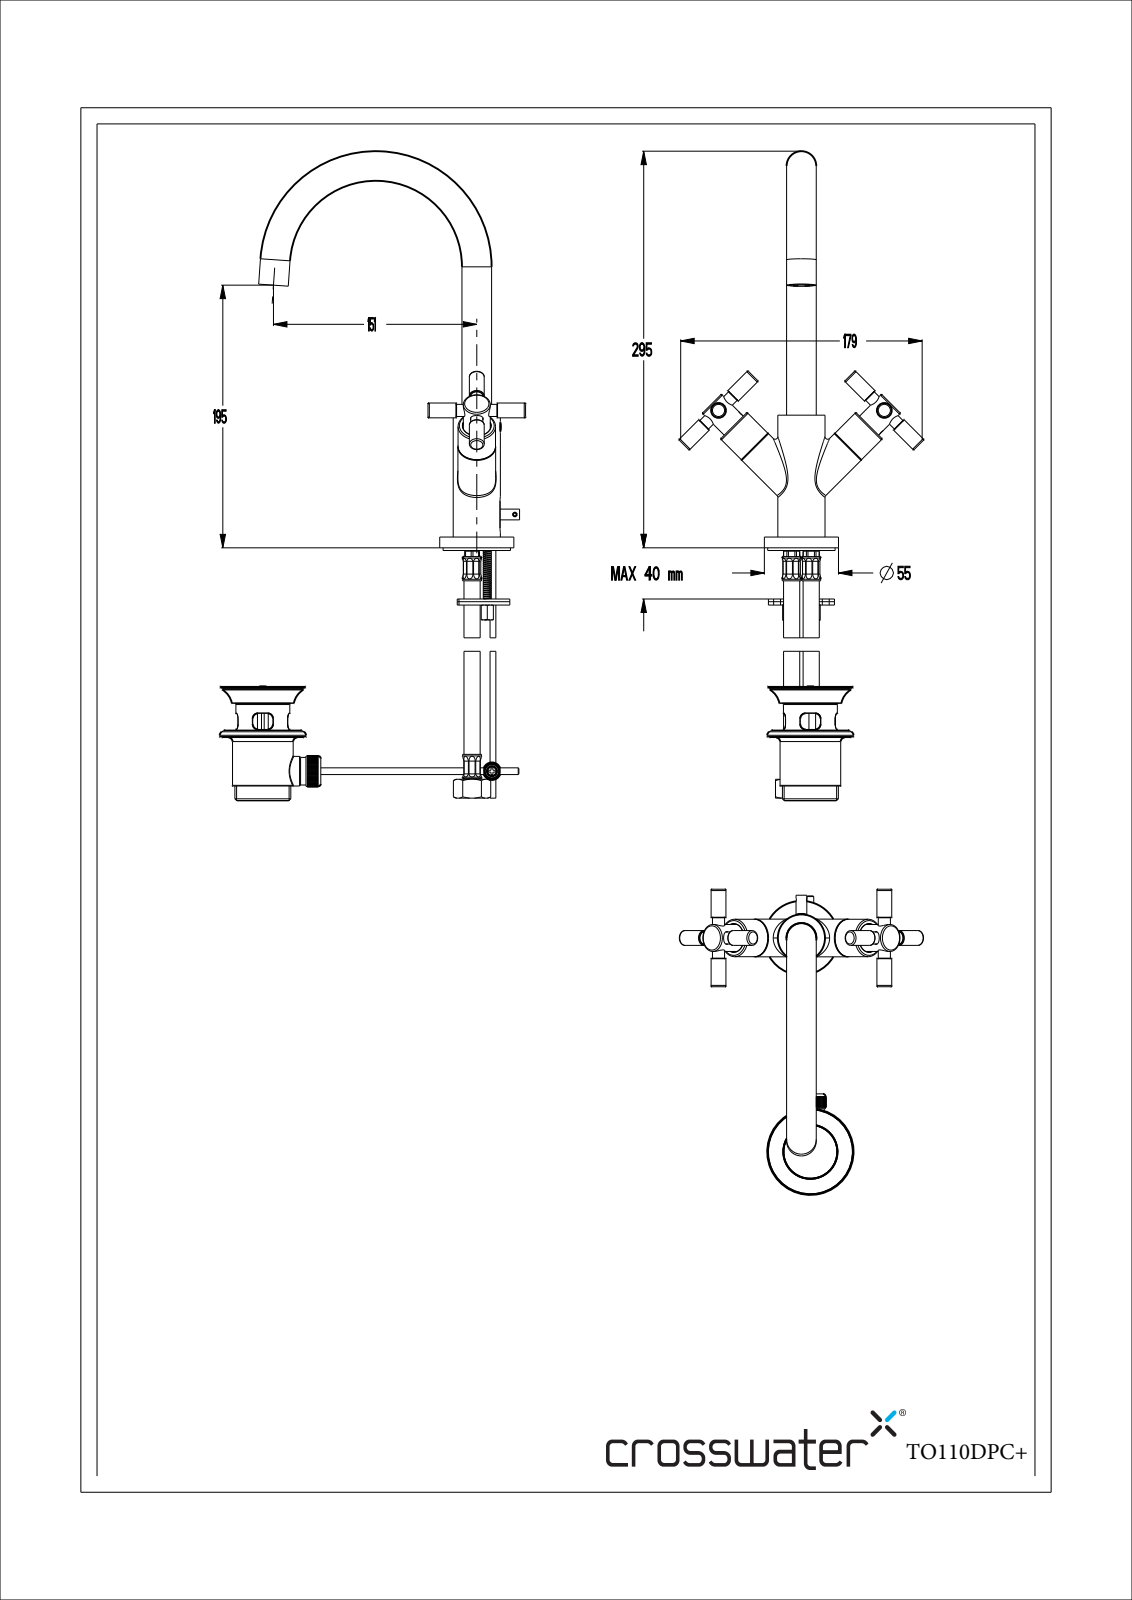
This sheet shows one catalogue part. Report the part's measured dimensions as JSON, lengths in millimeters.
{"part_name": "MSBR-42_1; MSBR-41_1; MSBR-36_2; MSBR-35_1 (+8 more)", "step_written_by": "PRO/ENGINEER BY PARAMETRIC TECHNOLOGY CORPORATION, 2009300 (CONFIG_CONTROL_DESIGN)", "units": "millimeters", "bodies": {"solids": 24, "faces": 842, "planar": 290, "cylindrical": 292, "other": 260}, "overall_size": [643, 198.04, 181.18], "volume_mm3": 169936, "surface_area_mm2": 115456, "round_holes": [[4.8, 4], [9.3, 4], [3.2, 2], [5, 2], [6, 2], [7, 2], [9, 2], [11, 2], [16, 2], [19, 2], [20, 2], [21, 2]], "round_bosses_or_shafts": [[11, 4], [9, 4], [6, 4], [4, 3], [28, 2], [27.8, 2], [22, 2], [20, 2]], "partial_cylinders_radius": [[2.85, 2], [3, 2], [9.55, 2], [3.3, 1], [8.5, 1]], "face_to_face_distances": [1, 6.5, 7, 97, 1.5, 90.5, 66.79, 0.5, 8, 45], "hole_center_spacings": [74, 87, 8.05, 9.16, 11.4, 11.72, 13, 15.77]}
